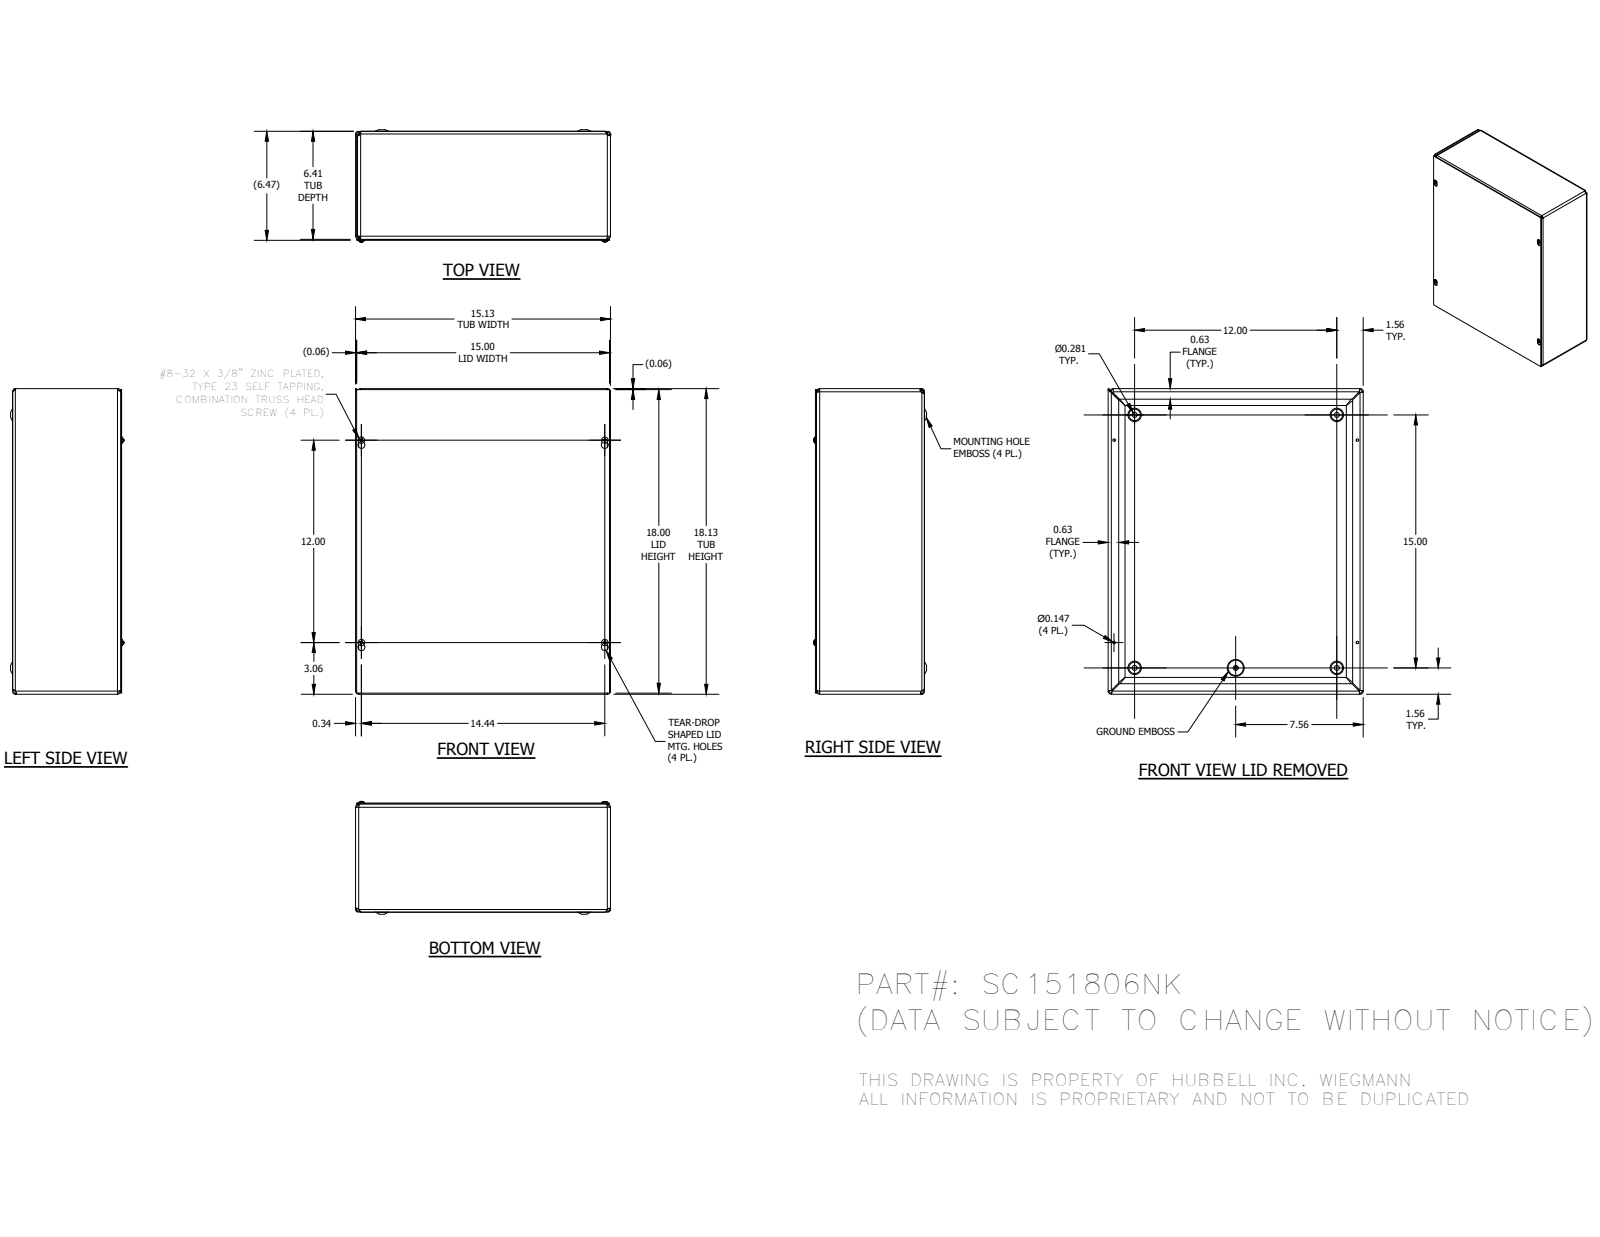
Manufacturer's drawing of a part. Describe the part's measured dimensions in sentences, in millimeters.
The part is named "SC1518BKP; SC151806NKWRA; SC1518LID; 34056 (+1 more)". Its 3-D file was written by "Autodesk Inventor 2014 (AUTOMOTIVE_DESIGN)". It is 7 solids with 357 faces: 132 planar, 67 cylindrical and 158 other. Overall it measures 460.38 by 384.18 by 170 millimeters. Its volume is 1 060 000 cubic millimeters and its surface area 1 355 000 square millimeters. Round holes: 4 of diameter 3.73, 4 of diameter 7.62, 1 of diameter 4.19. Round bosses or shafts: 4 of diameter 9.75, 4 of diameter 4.17, 1 of diameter 5.8. Partial cylindrical surfaces (rounded edges, fillets, slot ends): 12 of radius 3.17, 8 of radius 4.75, 4 of radius 1.4, 4 of radius 1.57, 4 of radius 2.38, 4 of radius 2.97, 4 of radius 3.15, 4 of radius 3.96. The main face-to-face distances are 1.57, 161.12, 162.69, 1.59, 162.71, 164.28, 382.6, 458.8, 384.17, 381.03. The hole center spacings are 49.09, 304.8, 344.29, 152.4, 337.9, 337.91, 366.71, 381.
